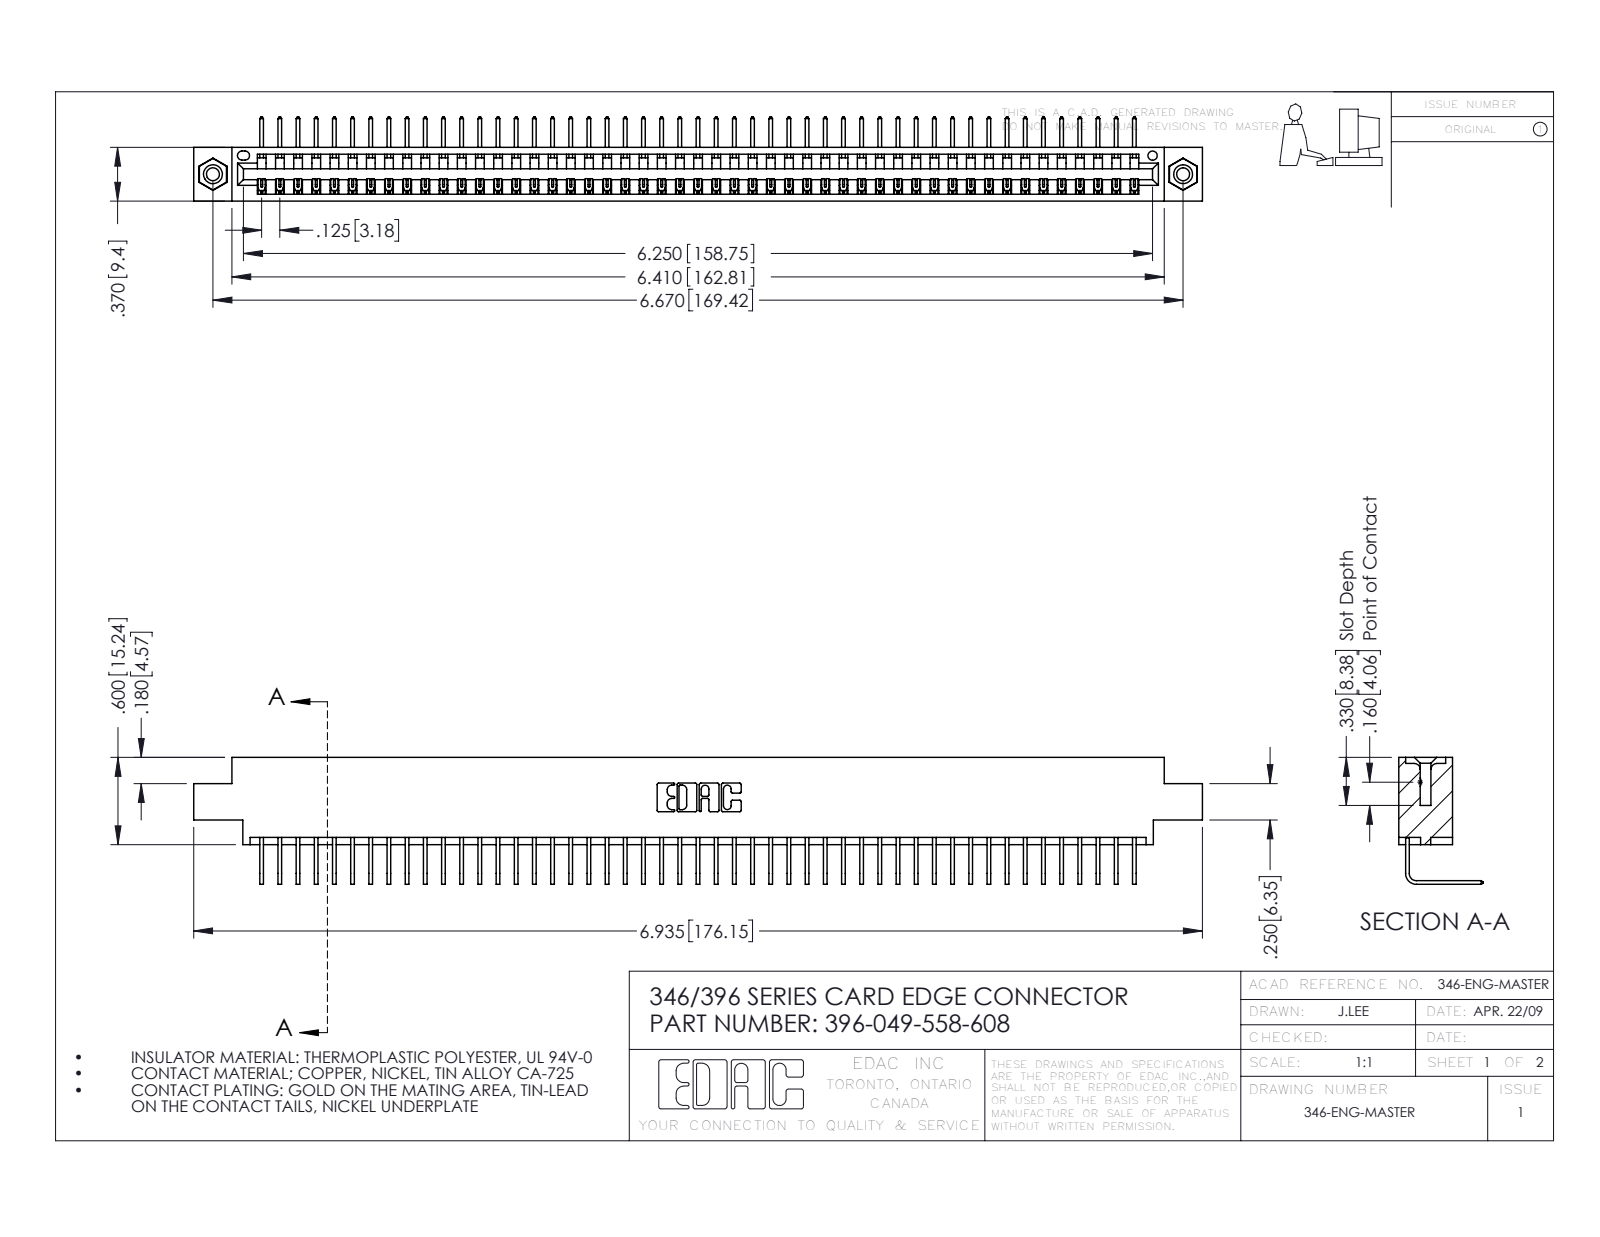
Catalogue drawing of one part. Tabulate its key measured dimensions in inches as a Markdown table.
| quantity | value |
| --- | --- |
| part name | 396-049-558-608; 345-250-001_345-250-003-102; 346 Part_0.170 Offset - 0.156 Dia-TI; 345-292-001_558 Tail - 2 |
| STEP written by | SolidWorks 2016 (CONFIG_CONTROL_DESIGN) |
| units | inches |
| bodies | 52 solids, 3126 faces (2170 planar, 940 cylindrical, 16 other) |
| overall size | 6.935 × 0.873 × 0.58 |
| volume | 1.032 in³ |
| surface area | 34.67 in² |
| round holes (diameter × count) | 0.089 × 2, 0.125 × 2, 0.156 × 2, 0.064 × 1 |
| round bosses / shafts (diameter × count) | 0.155 × 2 |
| partial cylindrical surfaces (radius × count) | 0.006 × 98, 0.01 × 22, 0.007 × 6, 0.031 × 6, 0.026 × 3, 0.031 × 2, 0.04 × 2, 0.014 × 1 |
| main face-to-face distances | 0.322, 0.048, 0.37, 0.25, 0.298, 0.025, 0.072, 0.222, 0.148, 0.1 |
| hole center spacings | 0.246, 6.461, 6.67 |
